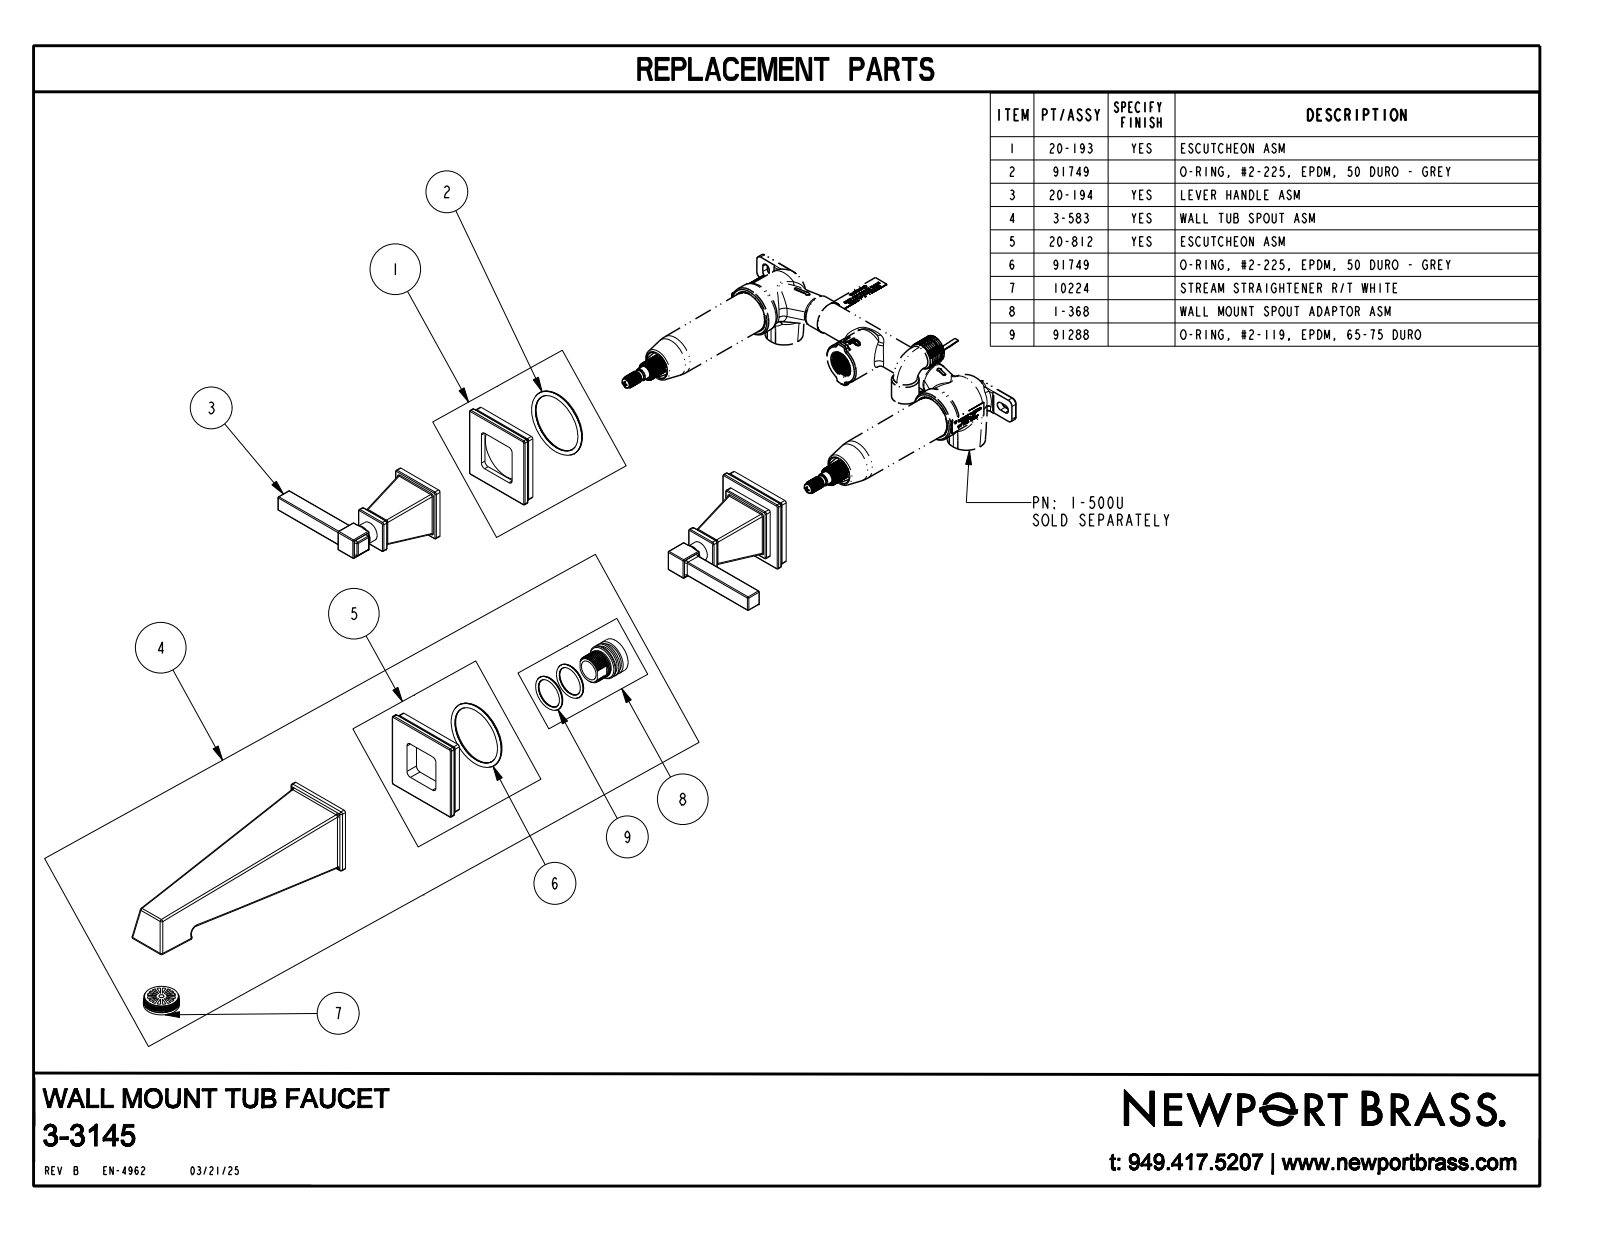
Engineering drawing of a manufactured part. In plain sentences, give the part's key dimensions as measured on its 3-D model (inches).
The part is named "3-3145_SW0001". Its 3-D file was written by "CREO PARAMETRIC BY PTC INC, 2018400 (AUTOMOTIVE_DESIGN)". It is 3 solids with 614 faces: 118 planar, 230 cylindrical and 266 other. Overall it measures 13.938 by 8.47 by 7.921 inches. Its volume is 32.91 cubic inches and its surface area 130.6 square inches. Round bosses or shafts: 2 of diameter 0.625, 2 of diameter 0.5. Partial cylindrical surfaces (rounded edges, fillets, slot ends): 84 of radius 0.03, 77 of radius 0.06, 16 of radius 0.09, 8 of radius 0.23, 4 of radius 0.317, 1 of radius 0.2. The main face-to-face distances are 0.41, 0.5, 0.42, 0.593, 0.093, 3.035, 3.535, 2.625, 3.125, 2.615.
